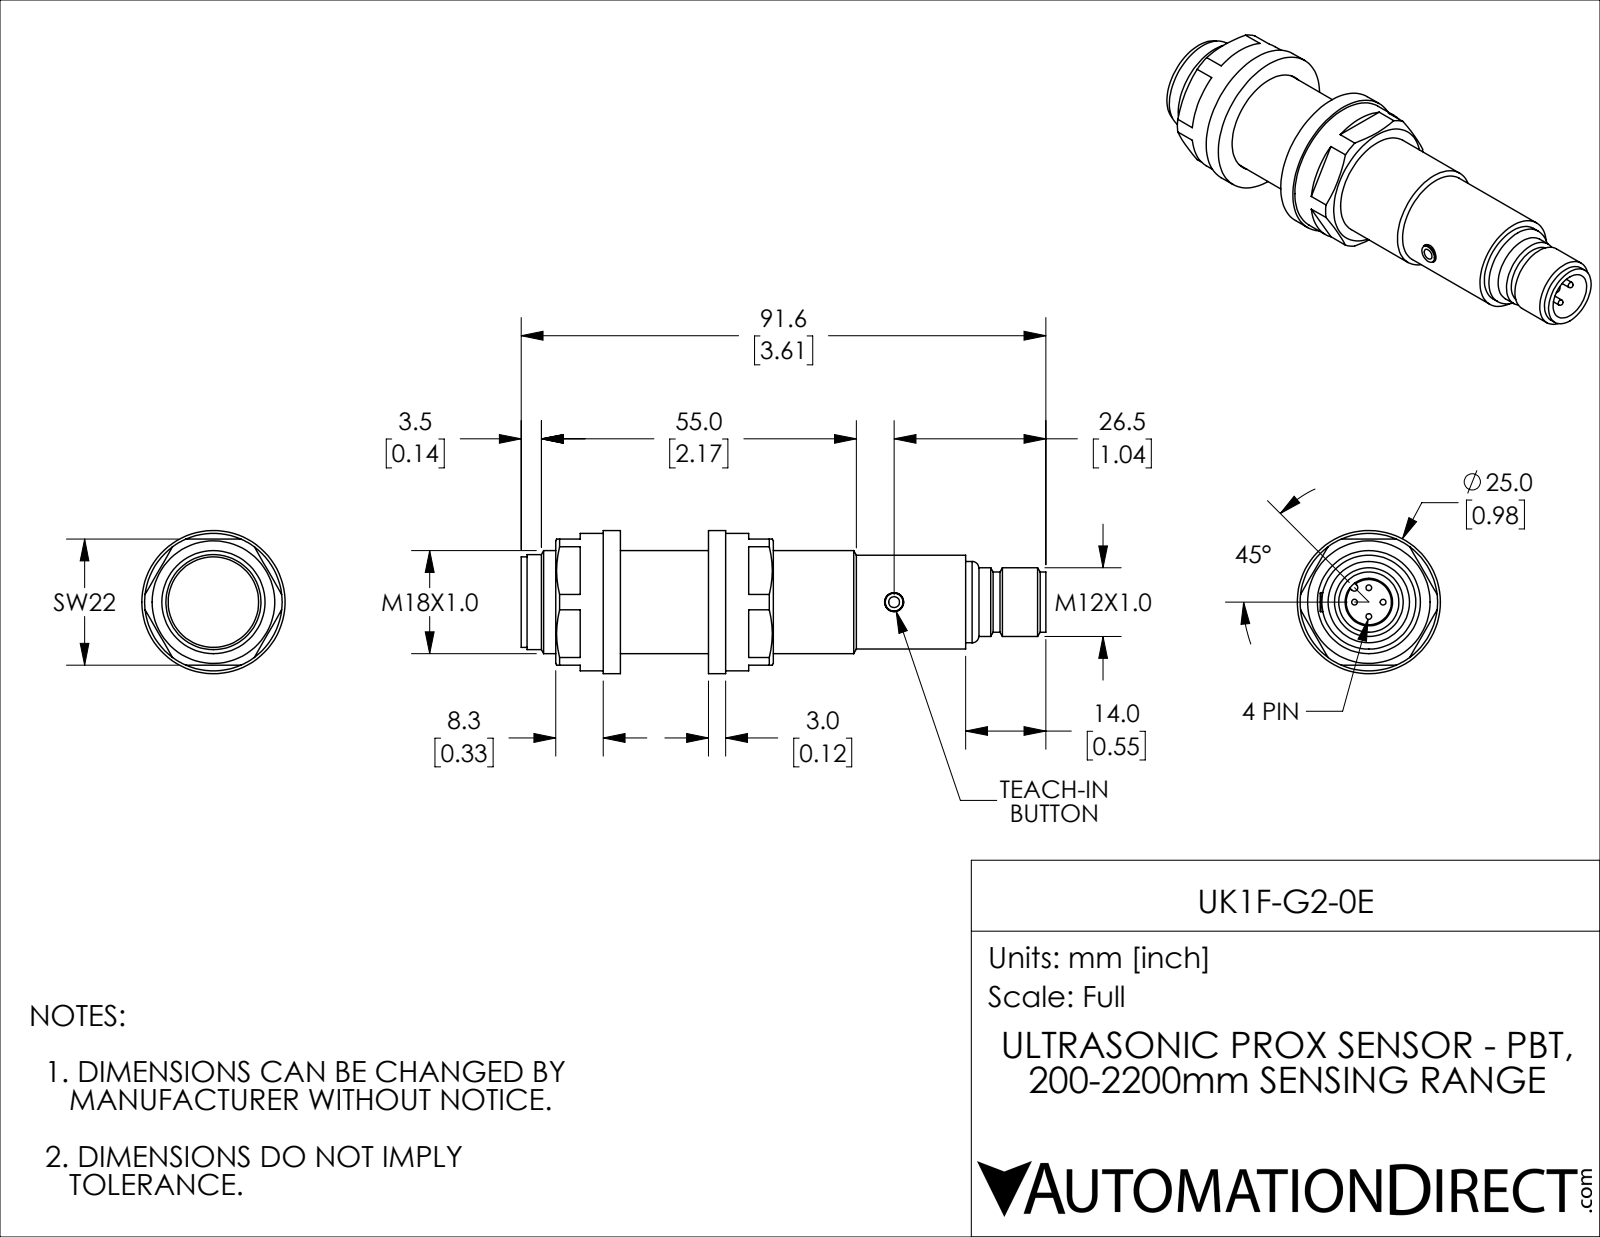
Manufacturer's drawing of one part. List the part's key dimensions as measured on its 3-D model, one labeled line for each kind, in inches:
Part name (STEP PRODUCT): UK1F-G2-0E
STEP written by: SolidWorks 2018 (AUTOMOTIVE_DESIGN)
Units: inches
Bodies: 6 solids, 123 faces (43 planar, 49 cylindrical, 31 other)
Overall size (bounding box): 3.606 × 0.984 × 0.984
Volume: 1.477 in³ · Surface area: 16.01 in²
Round holes (diameter × count): ⌀0.13 ×1, ⌀0.327 ×1, ⌀0.709 ×1, ⌀0.717 ×1
Round bosses / shafts (diameter × count): ⌀0.039 ×4, ⌀0.984 ×1, ⌀0.945 ×1, ⌀0.654 ×1, ⌀0.646 ×1, ⌀0.622 ×1, ⌀0.559 ×1, ⌀0.472 ×1
Partial cylindrical surfaces — rounded edges, fillets, slot ends (radius × count): R0.024 ×1
Main face-to-face distances: 0.118, 0.724, 0.843, 0.606, 0.866, 0.327, 0.445, 1.051, 1.169, 0.563
